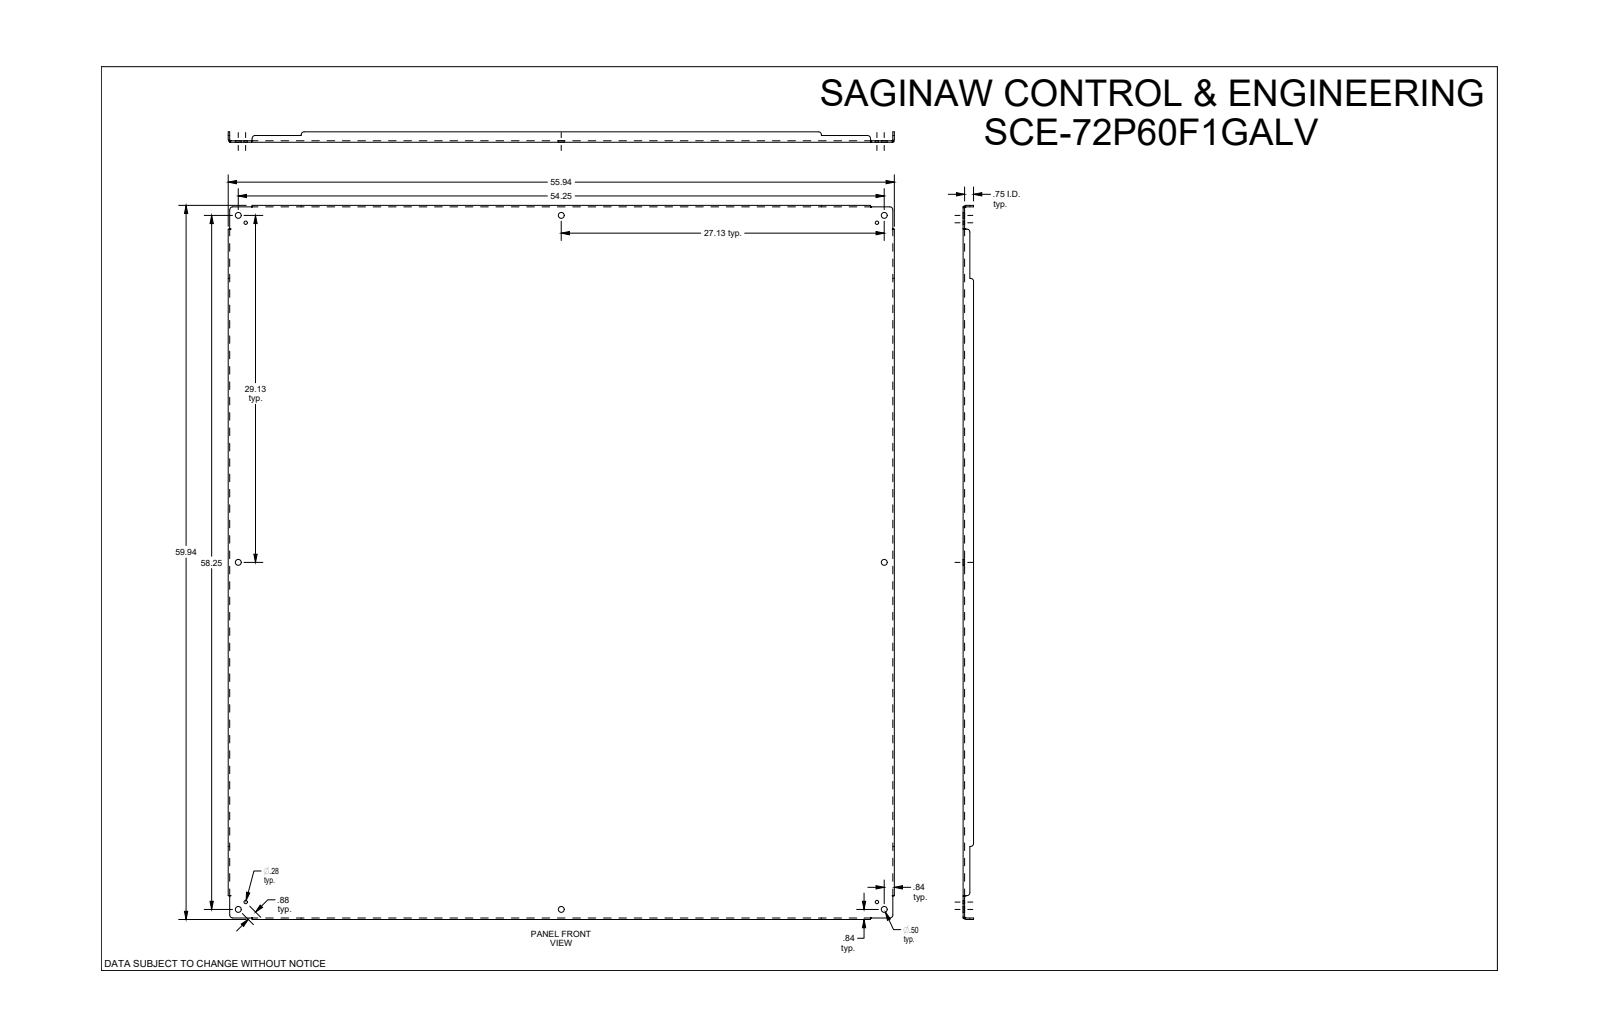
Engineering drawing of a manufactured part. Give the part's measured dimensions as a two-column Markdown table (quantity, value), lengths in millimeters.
| quantity | value |
| --- | --- |
| part name | SCE-72P60F1GALV |
| STEP written by | SolidWorks 2019 (CONFIG_CONTROL_DESIGN) |
| units | millimeters |
| bodies | 1 solid, 110 faces (46 planar, 40 cylindrical, 24 other) |
| overall size | 1522.4 × 1420.8 × 22.2 |
| volume | 7 137 000 mm³ |
| surface area | 4 516 000 mm² |
| round holes (diameter × count) | 12.7 × 8, 7.1 × 4 |
| partial cylindrical surfaces (radius × count) | 6.4 × 12, 2.8 × 4, 6 × 4 |
| main face-to-face distances | 3.2, 3.2, 1417.7, 1519.3, 1414.4, 1420.8, 1516, 1522.4, 19.1, 22.2 |
| hole center spacings | 22.2, 673.4, 689, 724.2, 739.8, 1010.9, 1362.3, 1463.9 |
